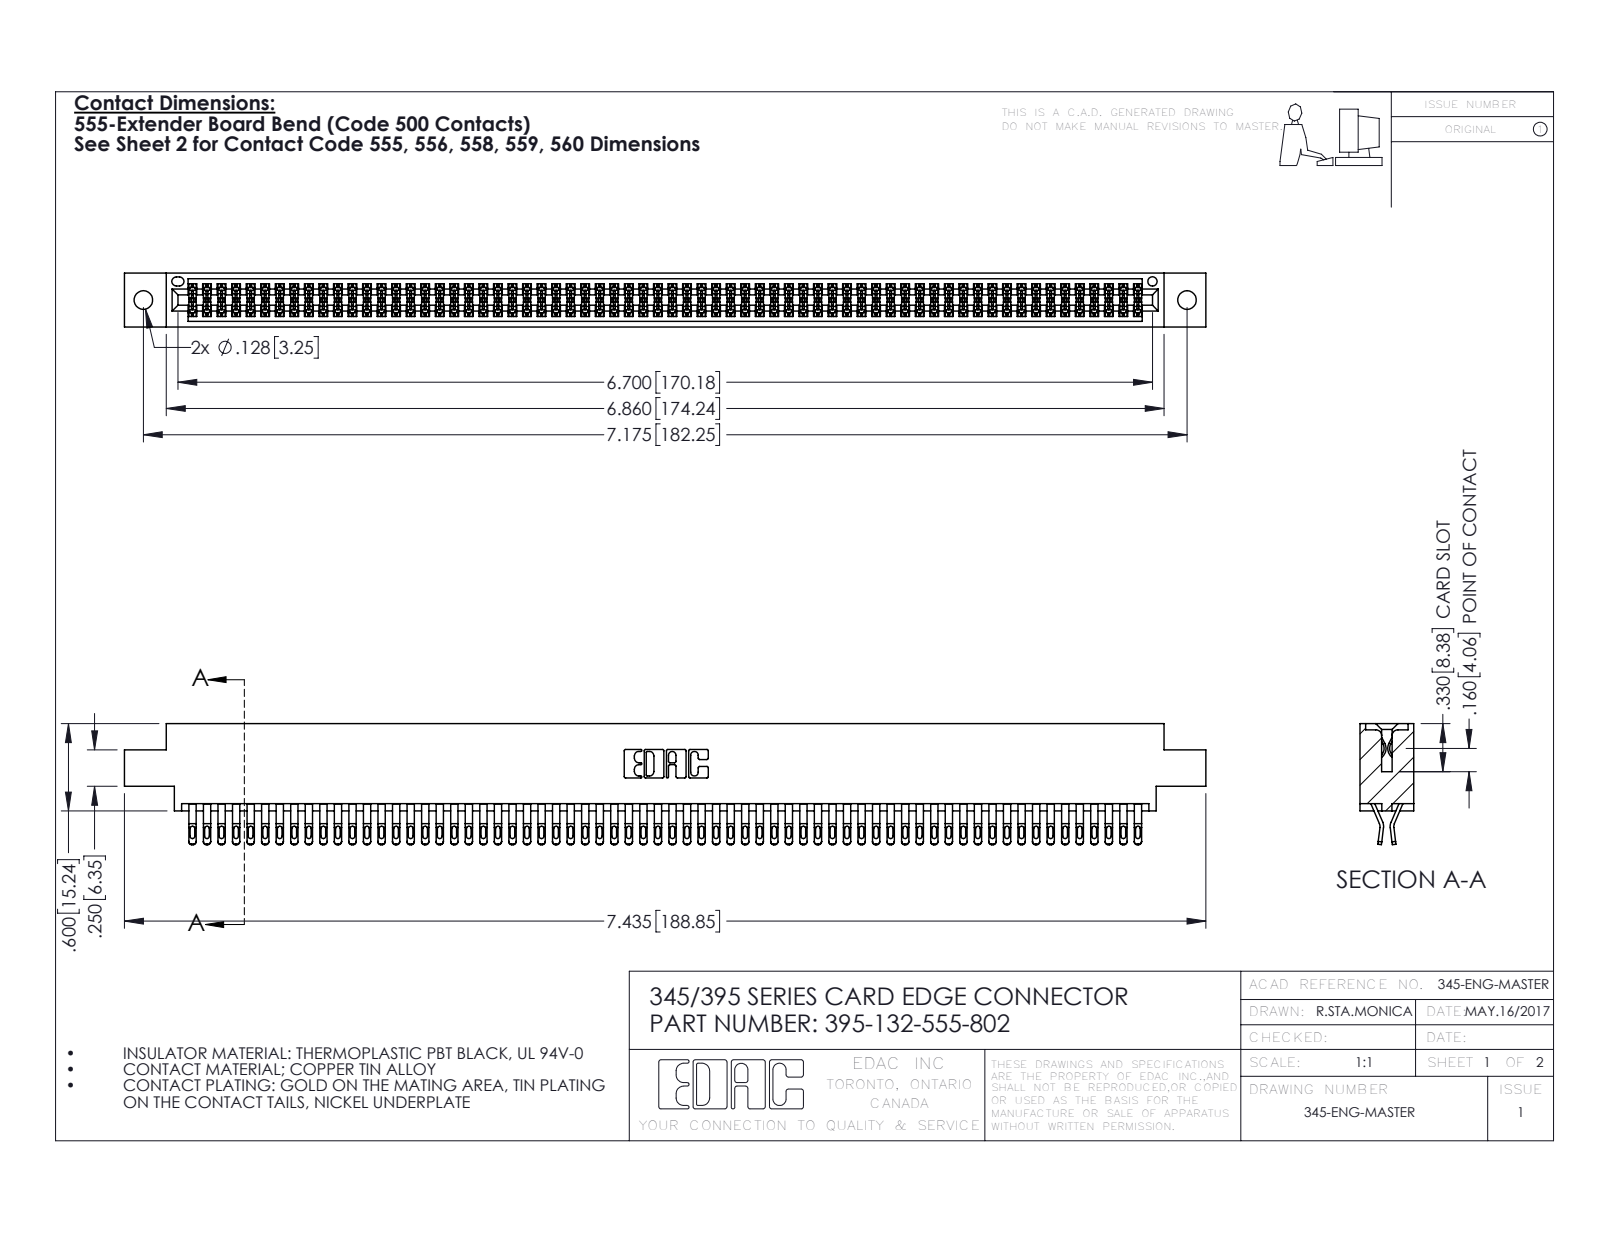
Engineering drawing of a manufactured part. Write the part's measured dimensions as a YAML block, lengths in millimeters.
part_name: "395-132-555-802; 345-292-001_555 Tail; 345 Part_0.170 Offset - 0.128 Dia"
step_written_by: "SolidWorks 2016 (CONFIG_CONTROL_DESIGN)"
units: millimeters
bodies: {solids: 133, faces: 7522, planar: 4176, cylindrical: 3346, other: 0}
overall_size: [188.8, 21.1, 9.4]
volume: 18800
surface_area: 29460
round_holes:
  - {diameter: 3.3, count: 2}
  - {diameter: 1.6, count: 1}
partial_cylinders:
  - {radius: 0.4, count: 330}
  - {radius: 0.5, count: 264}
  - {radius: 0.2, count: 198}
  - {radius: 0.3, count: 22}
  - {radius: 0.2, count: 6}
  - {radius: 0.8, count: 6}
  - {radius: 0.7, count: 3}
  - {radius: 0.3, count: 2}
face_to_face_distances: [7.6, 1.8, 0.6, 9.4, 5.1, 2.5, 6.9, 5.7, 4.4, 3.8]
hole_center_spacings: [6.9, 176.3, 182.2]
